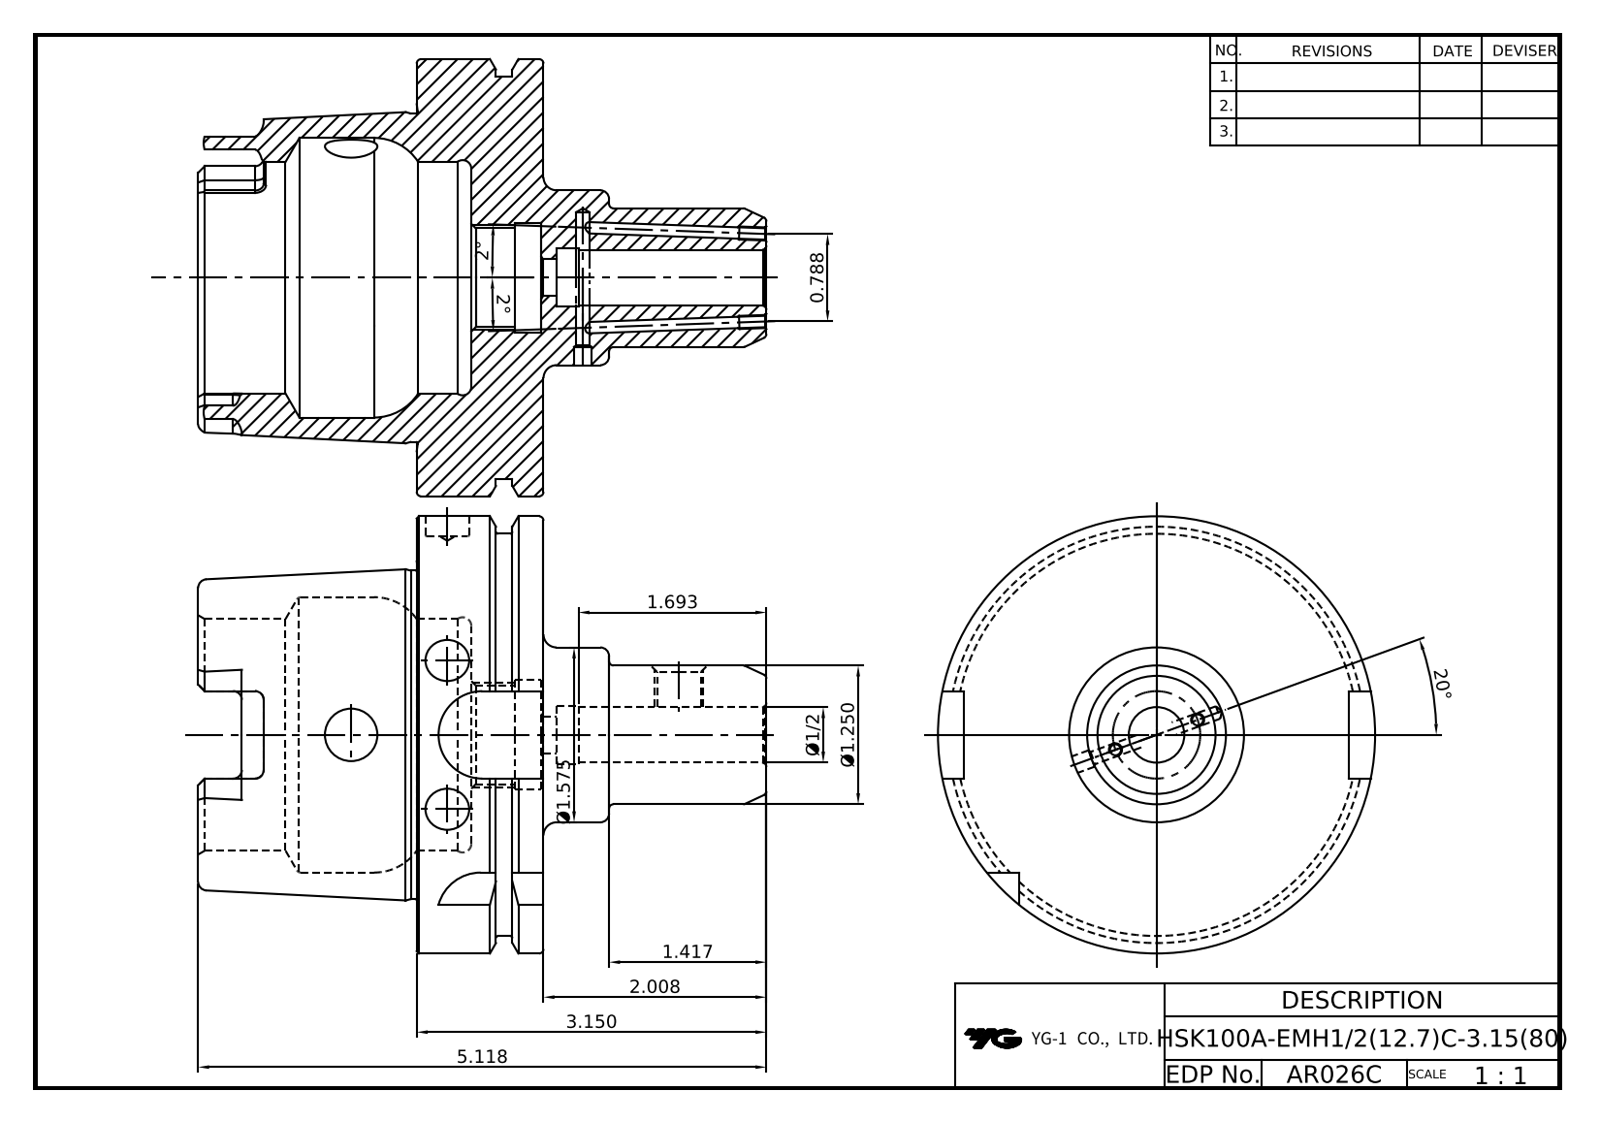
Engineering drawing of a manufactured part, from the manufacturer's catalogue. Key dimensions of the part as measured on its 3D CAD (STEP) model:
Part name (STEP PRODUCT): LO-HSK100A-EMH12.7C-80
STEP written by: Autodesk Inventor 2022 (AUTOMOTIVE_DESIGN)
Units: millimetres
Bodies: 1 solid, 137 faces (43 planar, 42 cylindrical, 52 other)
Overall size (bounding box): 130 × 100 × 100
Volume: 292 927 mm³ · Surface area: 57 660 mm²
Round holes (diameter × count): ⌀10 ×3, ⌀2.46 ×2, ⌀3 ×1, ⌀8.4 ×1, ⌀9.73 ×1, ⌀12 ×1, ⌀12.7 ×1, ⌀13.9 ×1, ⌀22.38 ×1, ⌀25 ×1, ⌀53 ×1, ⌀63 ×1
Round bosses / shafts (diameter × count): ⌀100 ×1, ⌀92 ×1, ⌀75.41 ×1, ⌀40 ×1, ⌀31.75 ×1
Partial cylindrical surfaces — rounded edges, fillets, slot ends (radius × count): R2 ×6, R4.88 ×4, R10 ×4
Main face-to-face distances: 29, 12.5, 16.5, 79, 62.5, 50, 88, 78.5, 28.5, 16
Hole centre spacings: 31, 53
